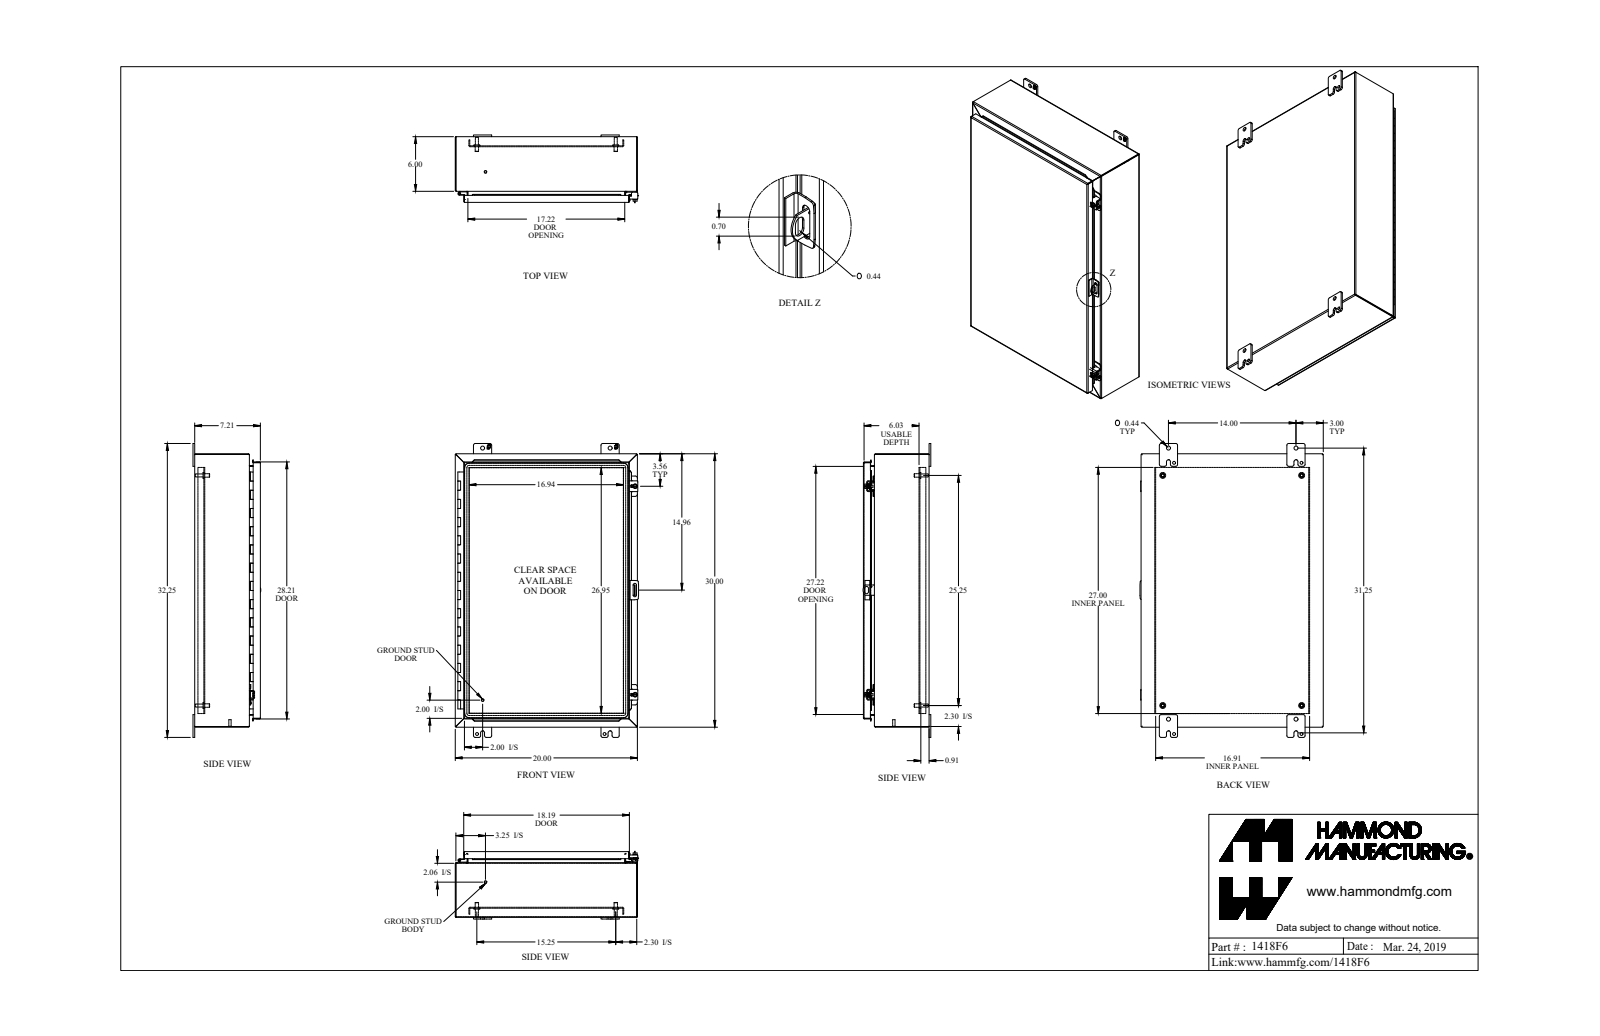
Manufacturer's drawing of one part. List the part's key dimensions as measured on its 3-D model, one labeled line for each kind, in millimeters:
Part name (STEP PRODUCT): 1418F6
STEP written by: SolidWorks 2019 (AUTOMOTIVE_DESIGN)
Units: millimetres
Bodies: 38 solids, 1046 faces (717 planar, 275 cylindrical, 54 other)
Overall size (bounding box): 819.2 × 511.2 × 188.9
Volume: 3 515 000 mm³ · Surface area: 3 569 000 mm²
Round holes (diameter × count): ⌀8 ×4, ⌀11.1 ×4, ⌀12.7 ×4, ⌀5.4 ×2, ⌀6.7 ×2, ⌀7.8 ×2, ⌀9.5 ×2, ⌀11.3 ×2, ⌀3.2 ×1, ⌀4.7 ×1
Round bosses / shafts (diameter × count): ⌀16.5 ×4, ⌀9.5 ×4, ⌀8.4 ×4, ⌀25.4 ×2, ⌀12.7 ×2, ⌀9.9 ×2, ⌀7.1 ×2, ⌀6.4 ×2
Partial cylindrical surfaces — rounded edges, fillets, slot ends (radius × count): R4.8 ×26, R0.9 ×20, R2.7 ×20, R1.2 ×13, R3.6 ×13, R0.2 ×8, R1.1 ×8, R2 ×8
Main face-to-face distances: 1.8, 180.7, 178.8, 23.8, 182.5, 25.6, 2.4, 154.5, 152.6, 26.2
Hole centre spacings: 44.1, 355.6, 387.4, 755.7, 835.2, 749.2, 749.2, 753.9
